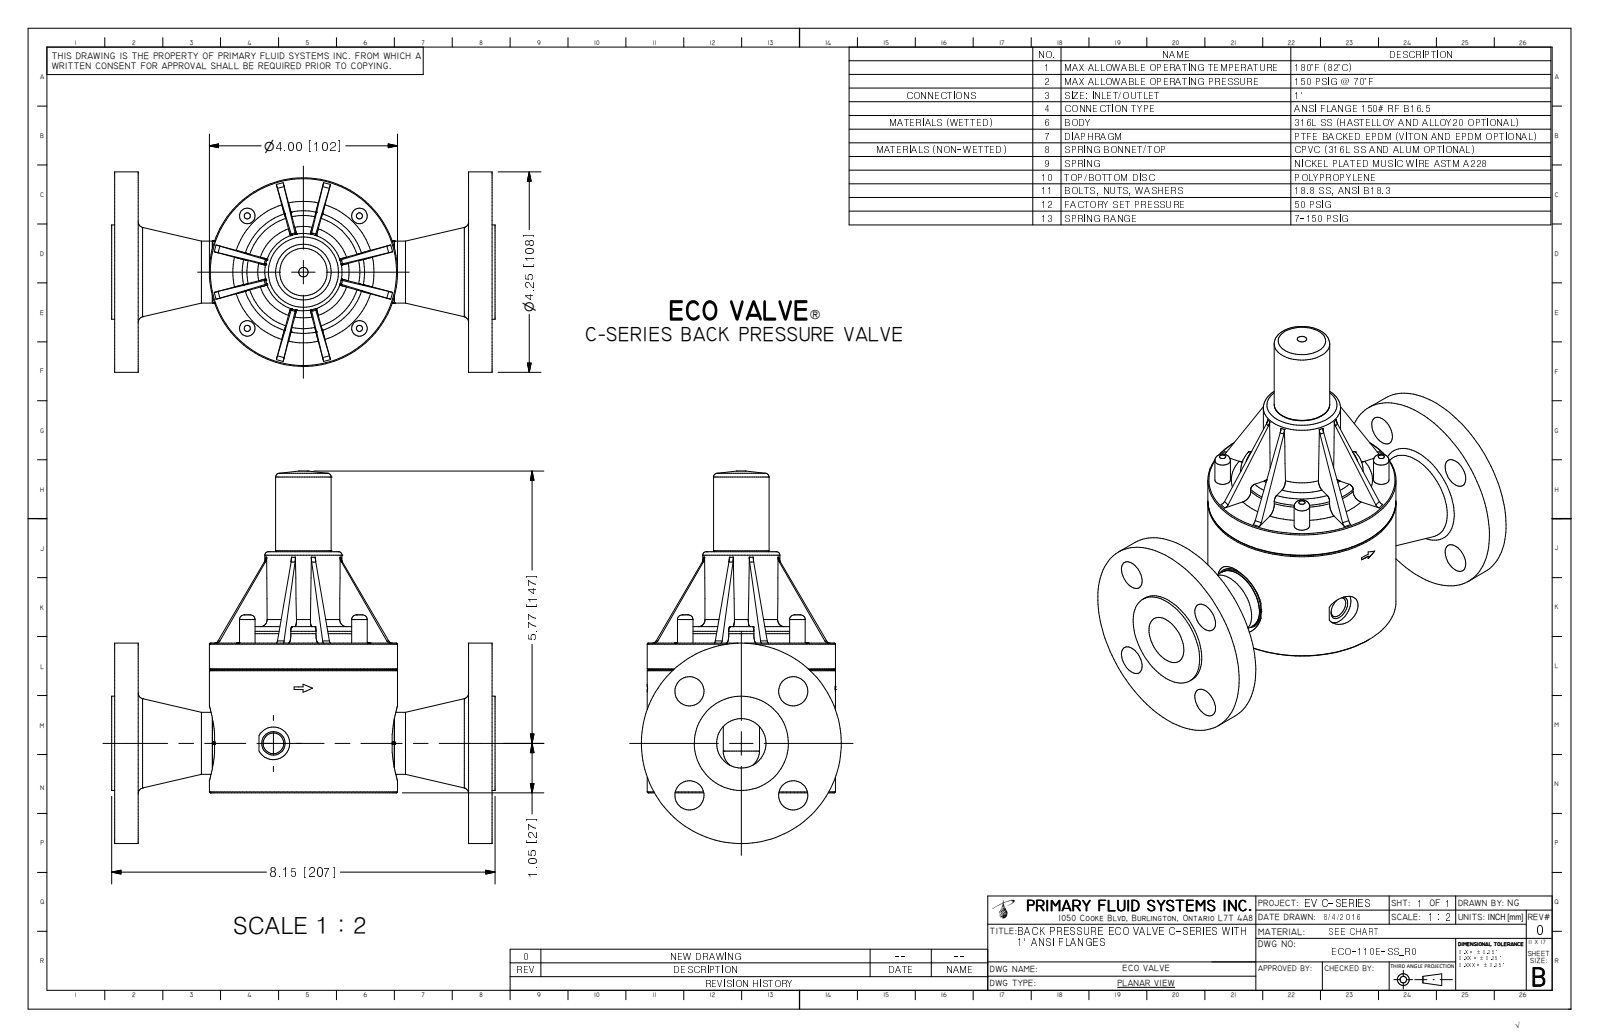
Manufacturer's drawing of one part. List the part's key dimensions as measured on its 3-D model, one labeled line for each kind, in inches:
Part name (STEP PRODUCT): ECO-110E-SS_R0
STEP written by: Autodesk Inventor 2009 (AUTOMOTIVE_DESIGN)
Units: inches
Bodies: 1 solid, 247 faces (109 planar, 68 cylindrical, 70 other)
Overall size (bounding box): 8.15 × 7.899 × 4.25
Volume: 63.44 in³ · Surface area: 207.6 in²
Round holes (diameter × count): ⌀0.23 ×4, ⌀0.4 ×4, ⌀0.62 ×4, ⌀0.257 ×1, ⌀0.438 ×1, ⌀0.691 ×1, ⌀1.049 ×1
Round bosses / shafts (diameter × count): ⌀0.33 ×4, ⌀0.256 ×4, ⌀4.25 ×1, ⌀4 ×1, ⌀2.6 ×1, ⌀2 ×1, ⌀1.64 ×1, ⌀1.315 ×1
Partial cylindrical surfaces — rounded edges, fillets, slot ends (radius × count): R0.1 ×8, R0.128 ×4, R0.129 ×3, R0.2 ×3, R1.999 ×1
Main face-to-face distances: 0.5, 7.525, 8.025, 7.025, 0.063, 0.563, 7.588, 8.088, 3.174, 8.15
Hole centre spacings: 1.56, 2.206, 2.385, 2.385, 2.386, 2.386, 3.12, 3.373
